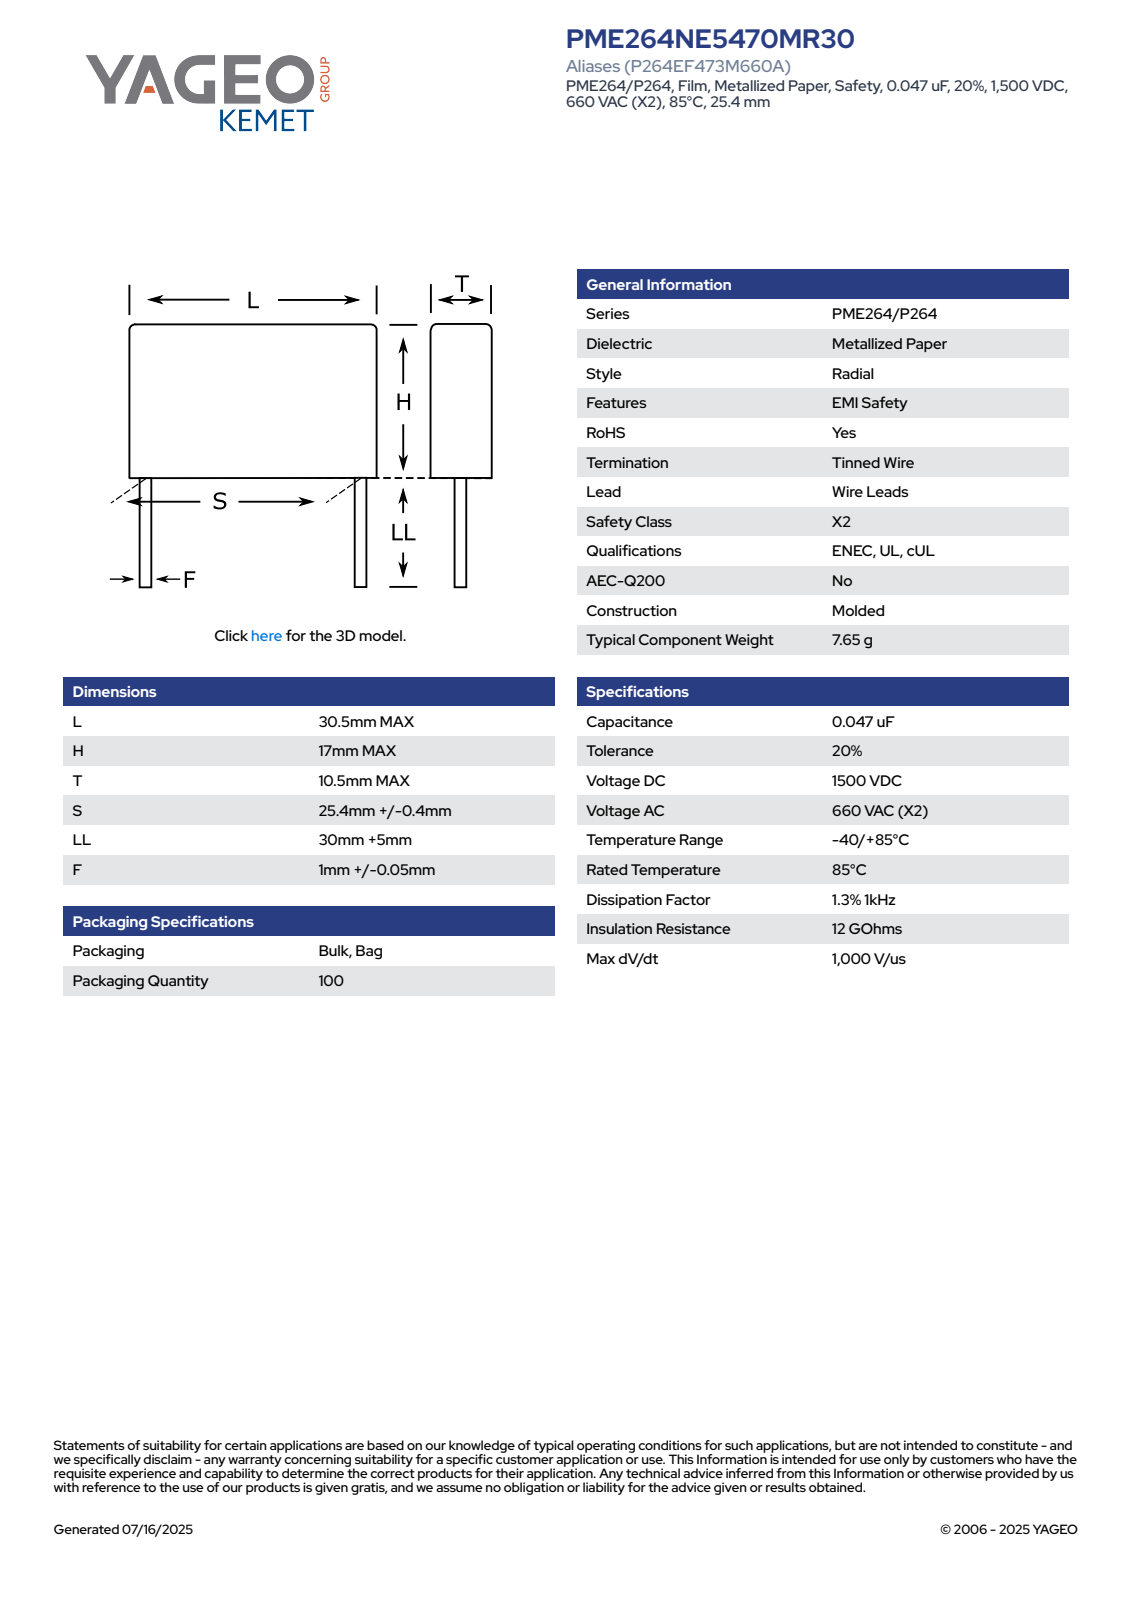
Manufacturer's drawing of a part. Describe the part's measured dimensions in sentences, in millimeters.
The part is named "CFR_MOLDED_30.5X17X10.5_L30.5H17T10.5S25.4LL35F1.05". Its 3-D file was written by "SolidWorks 2021 (AUTOMOTIVE_DESIGN)". It is 4 solids with 73 faces: 65 planar, 8 cylindrical and 0 other. Overall it measures 52 by 30.5 by 10.51 millimeters. Its volume is 5 501 cubic millimeters and its surface area 2 292 square millimeters. Round bosses or shafts: 2 of diameter 1.05. Partial cylindrical surfaces (rounded edges, fillets, slot ends): 4 of radius 0.5. The main face-to-face distances are 10.5, 17, 30.5, 10.51, 35, 52, 44.86, 9.86, 7.14, 42.13.
